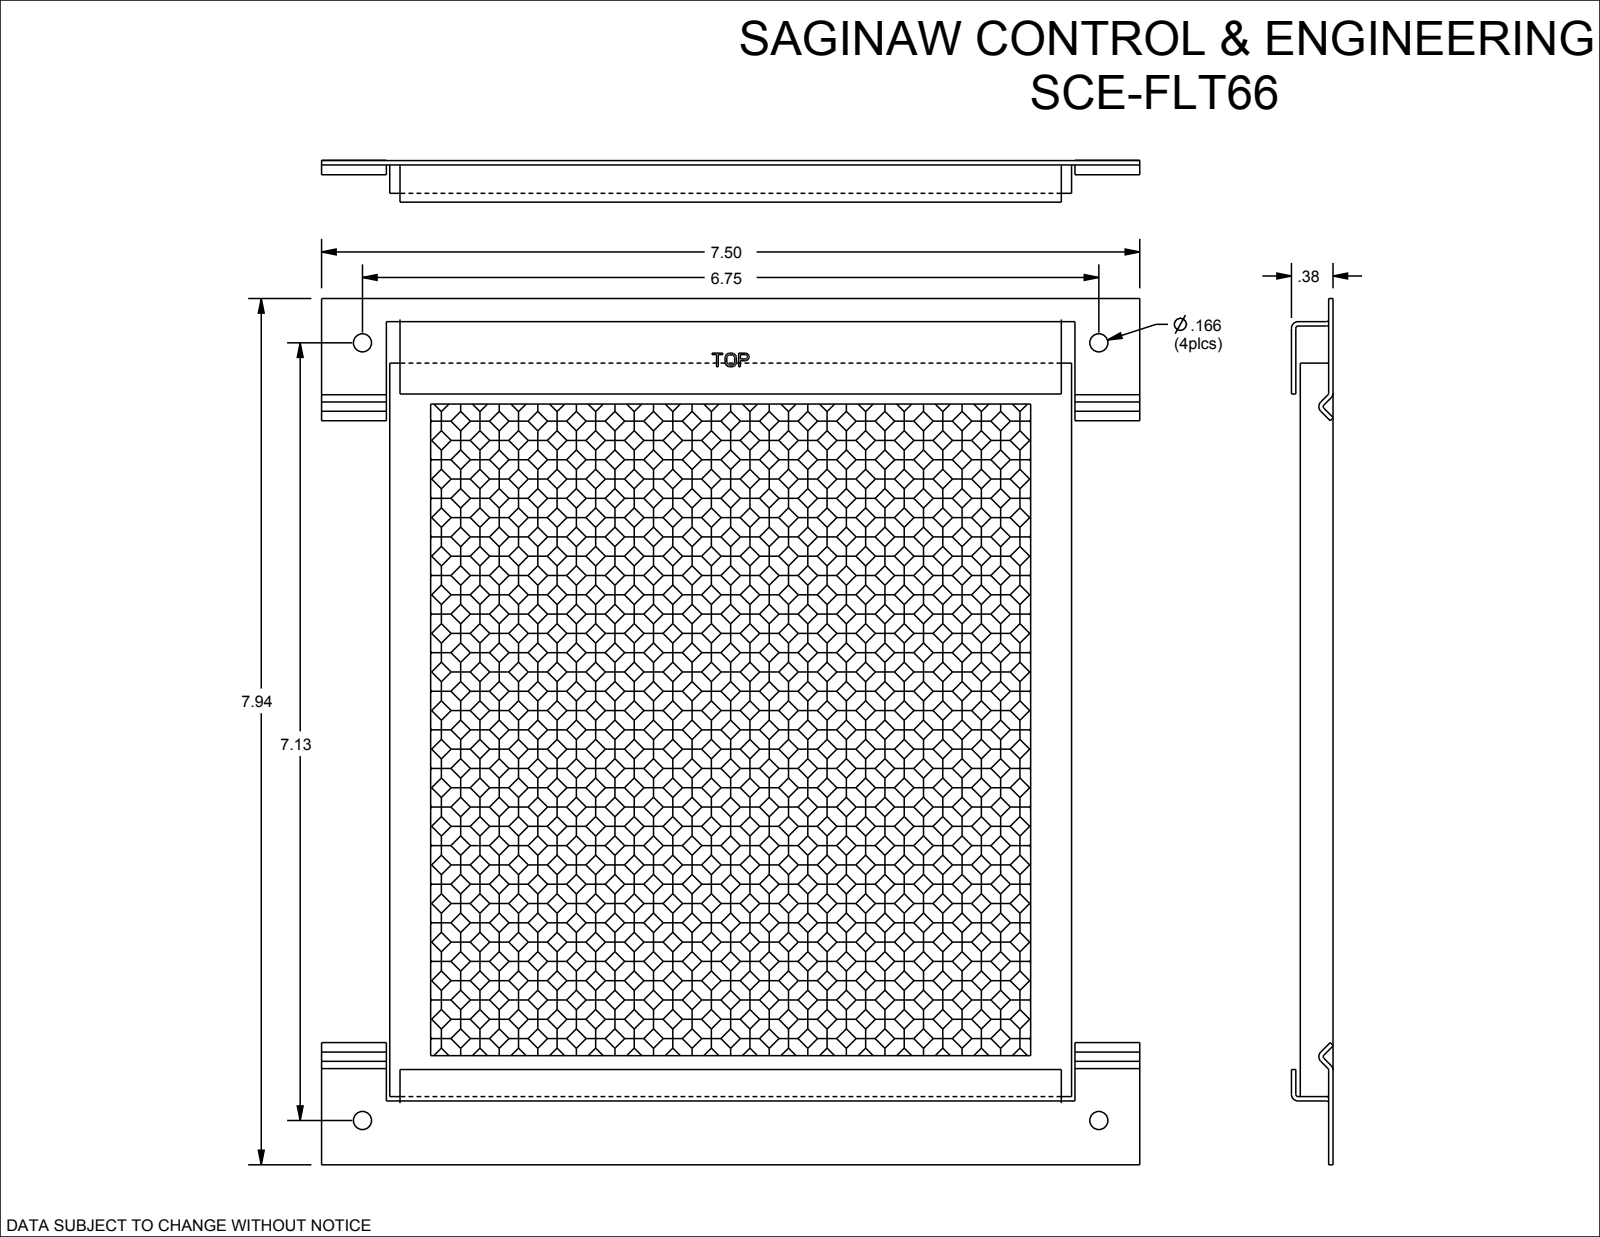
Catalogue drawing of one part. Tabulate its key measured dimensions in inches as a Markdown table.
| quantity | value |
| --- | --- |
| part name | SCE-FLT66 |
| STEP written by | SolidWorks 2019 (CONFIG_CONTROL_DESIGN) |
| units | inches |
| bodies | 3 solids, 3428 faces (1224 planar, 2204 cylindrical, 0 other) |
| overall size | 7.937 × 7.5 × 0.384 |
| volume | 6.15 in³ |
| surface area | 149.2 in² |
| round holes (diameter × count) | 0.166 × 4 |
| round bosses / shafts (diameter × count) | 0.125 × 49, 0.125 × 15 |
| partial cylindrical surfaces (radius × count) | 0.02 × 8, 0.06 × 8 |
| main face-to-face distances | 0.04, 0.3, 0.14, 0.16, 0.02, 0.16, 0.14, 0.26, 0.12, 0.1 |
| hole center spacings | 7.125, 6.75, 6.75, 9.815, 9.815 |
